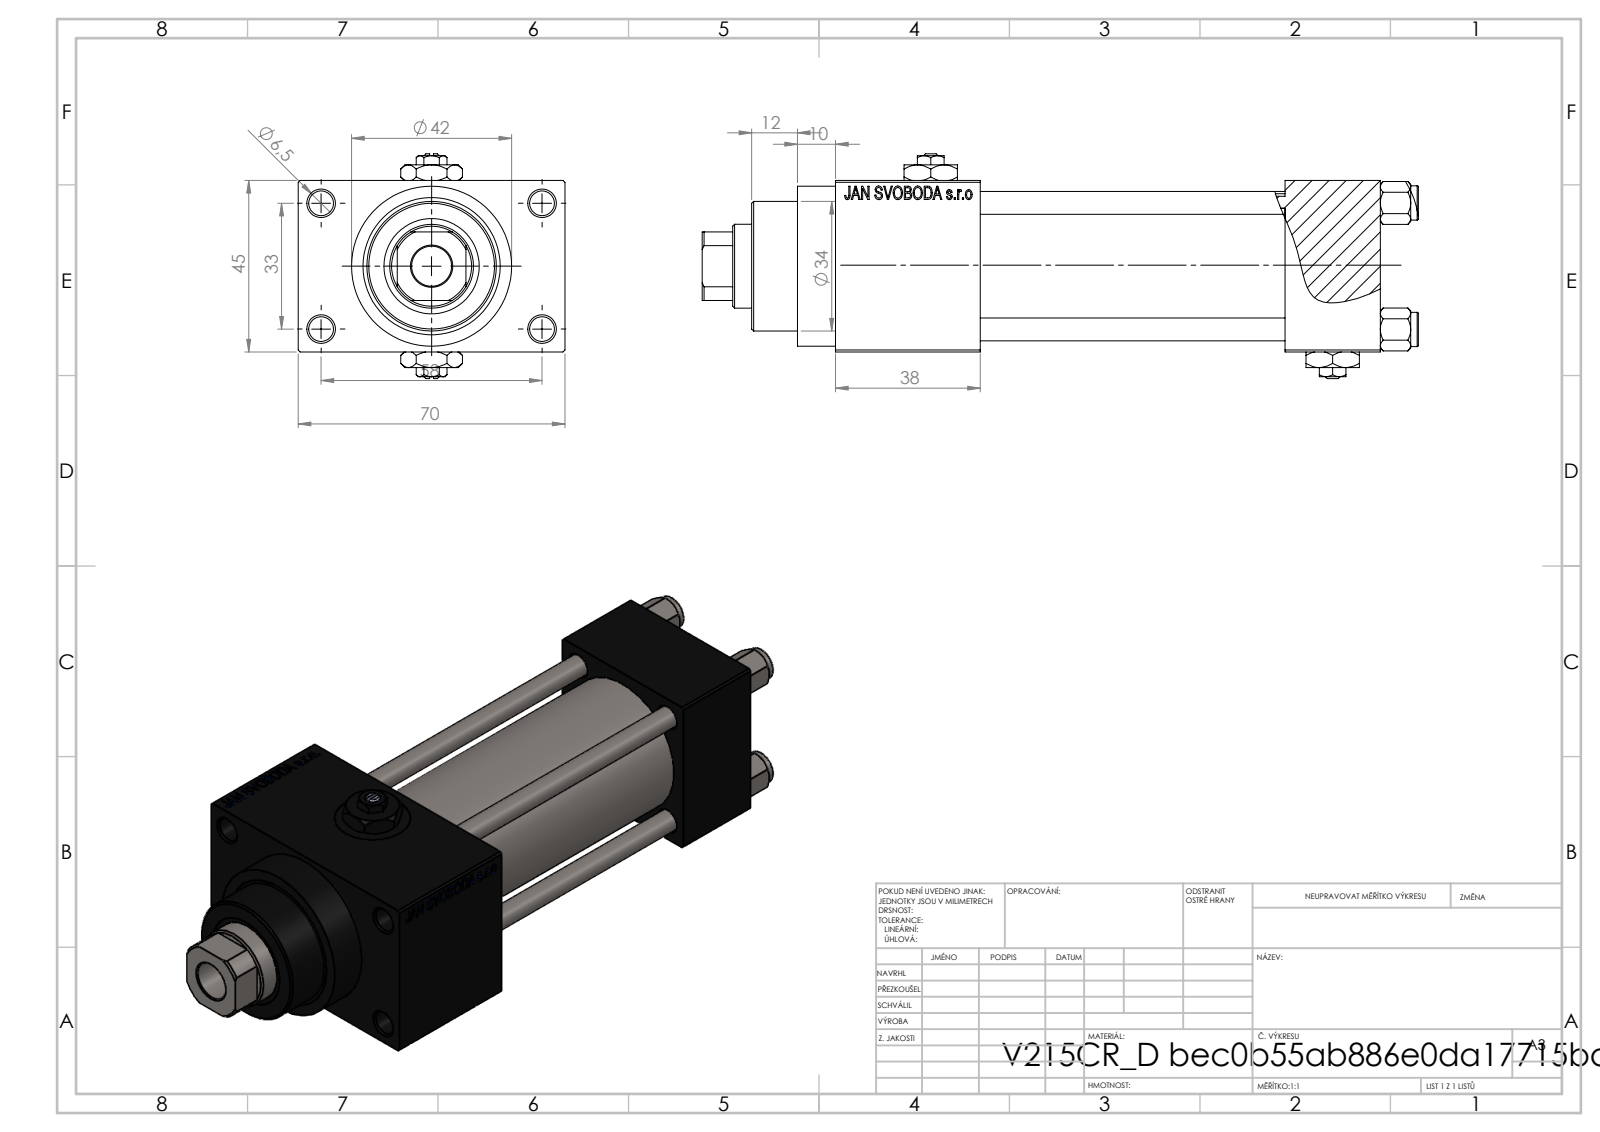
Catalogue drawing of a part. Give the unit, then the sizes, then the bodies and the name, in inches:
Units: inches
Overall size (bounding box): 7.402 × 2.756 × 2.323
Round holes (diameter × count): ⌀0.236 ×4, ⌀0.256 ×4, ⌀0.276 ×2, ⌀0.518 ×2, ⌀0.787 ×2, ⌀0.413 ×1, ⌀0.866 ×1, ⌀0.945 ×1, ⌀0.984 ×1, ⌀1.26 ×1, ⌀1.299 ×1
Round bosses / shafts (diameter × count): ⌀0.354 ×4, ⌀1.654 ×1, ⌀1.496 ×1, ⌀1.339 ×1
Partial cylindrical surfaces — rounded edges, fillets, slot ends (radius × count): R0.413 ×1
Main face-to-face distances: 1.772, 0.984, 0.492, 2.264, 3.15, 4.134, 4.646, 2.756, 1.496, 5.63
Hole centre spacings: 0.488, 0.924, 1.307, 1.314, 1.392, 1.795, 2.219, 1.299
Volume: 16.53 in³ · Surface area: 141.8 in²
Bodies: 13 solids, 1189 faces (540 planar, 89 cylindrical, 560 other)
Part name (STEP PRODUCT): V215_VC_A; Zatka_pro_OIL_PORT; NUT_M5_D; V215CR_D_Body (+2 more)
STEP written by: SolidWorks 2019 (CONFIG_CONTROL_DESIGN)
